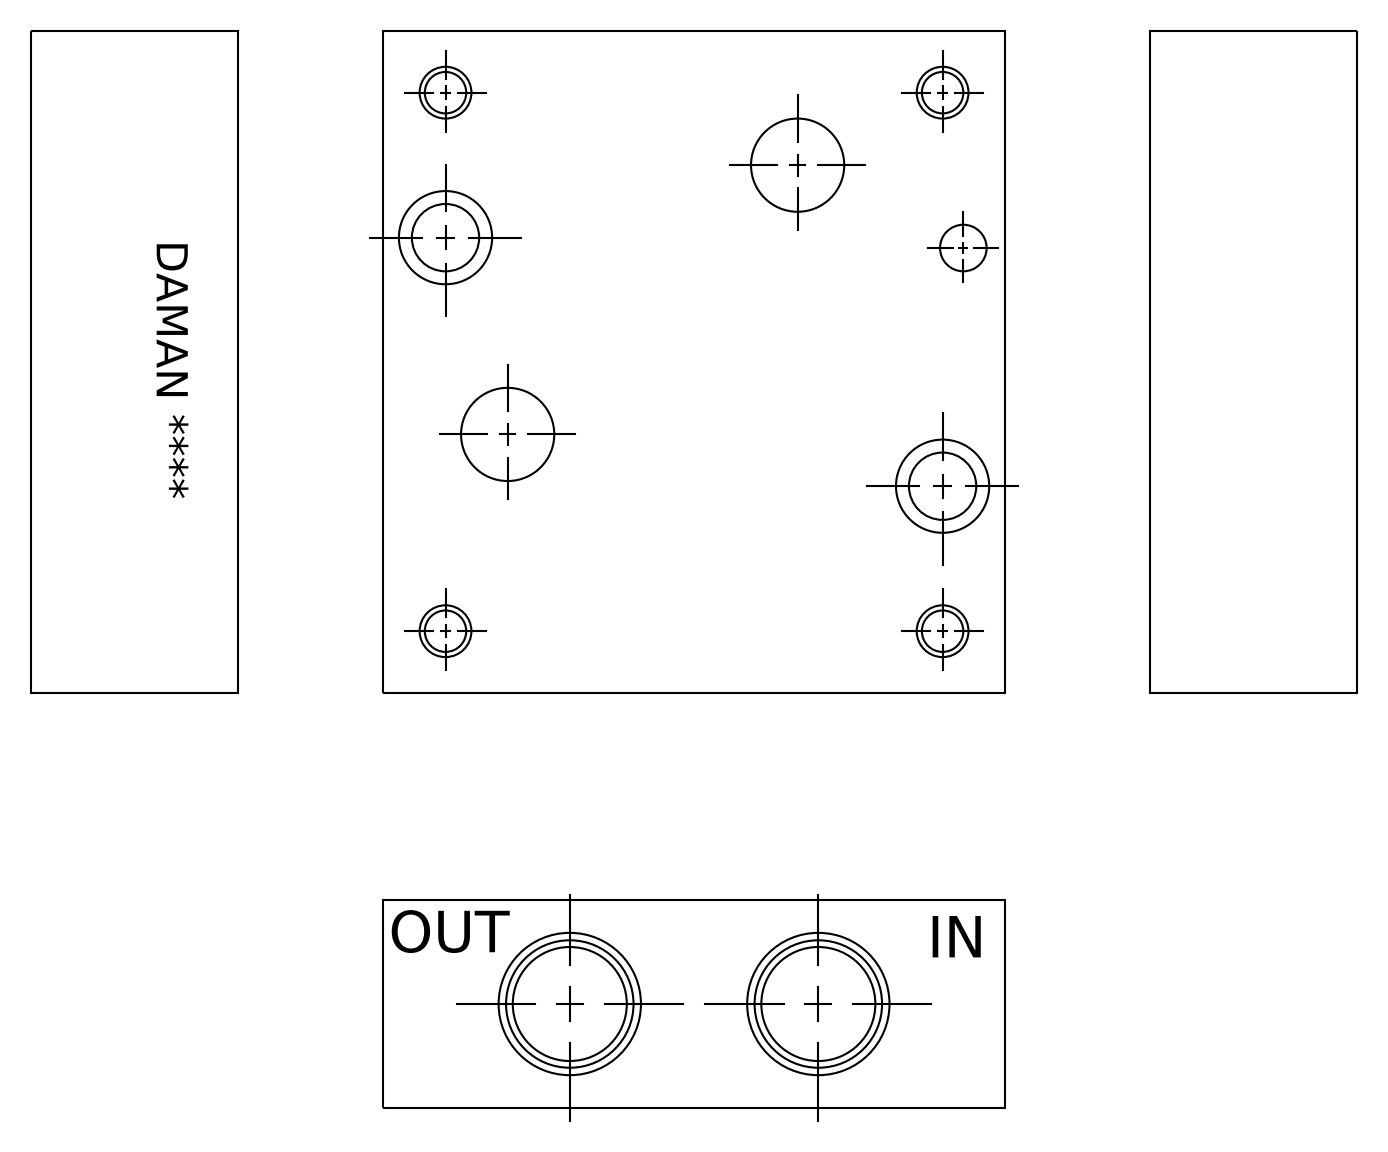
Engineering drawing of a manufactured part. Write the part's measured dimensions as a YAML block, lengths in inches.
part_name: "Part_A2F06SPS8P_3D"
step_written_by: "Autodesk Inventor 2020 (AUTOMOTIVE_DESIGN)"
units: inches
bodies: {solids: 1, faces: 436, planar: 269, cylindrical: 19, other: 148}
overall_size: [4, 3.75, 1.25]
volume: 17.03
surface_area: 61.33
round_holes:
  - {diameter: 0.257, count: 4}
  - {diameter: 0.312, count: 4}
  - {diameter: 0.406, count: 2}
  - {diameter: 0.562, count: 2}
  - {diameter: 0.625, count: 2}
  - {diameter: 0.688, count: 2}
  - {diameter: 0.85, count: 2}
  - {diameter: 0.281, count: 1}
face_to_face_distances: [1.25, 3.75, 4, 0.605, 3.395, 0.69, 0.56, 3.748, 0.32, 0.37]
hole_center_spacings: [3, 3.25, 3.826, 4.423, 0.875, 0.875, 0.945, 0.978]
